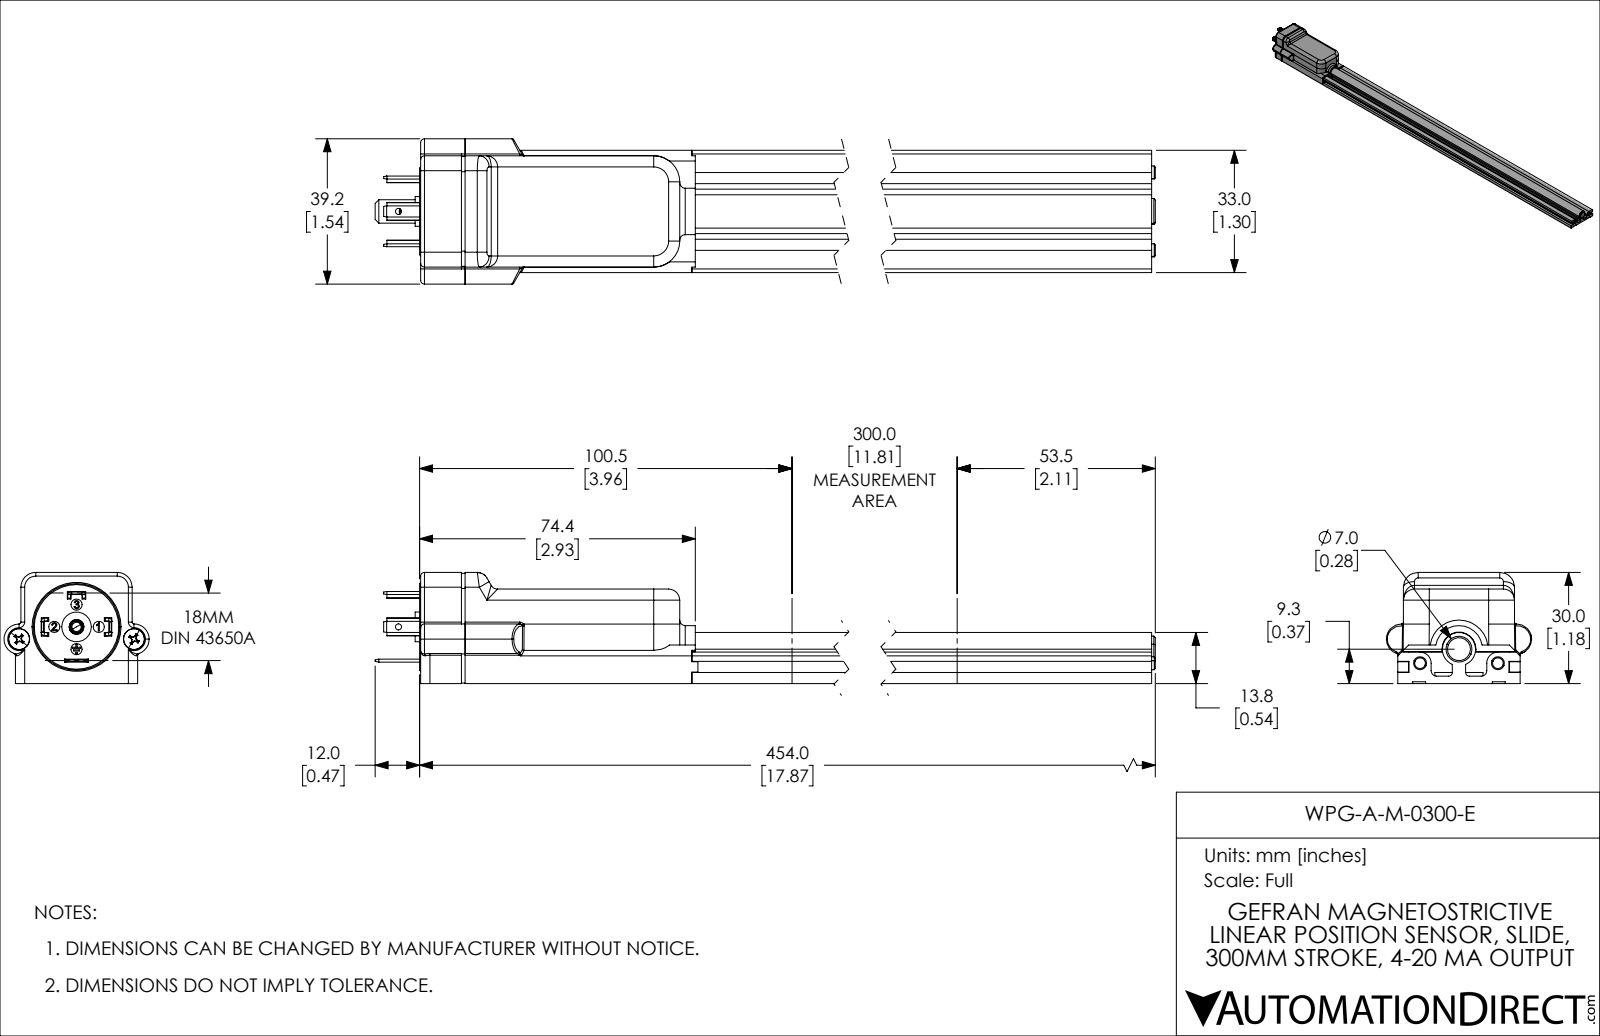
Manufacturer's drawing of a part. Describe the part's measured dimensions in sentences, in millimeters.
The part is named "WPG-A-M-0300-E". Its 3-D file was written by "SolidWorks 2021 (CONFIG_CONTROL_DESIGN)". It is 15 solids with 589 faces: 371 planar, 139 cylindrical and 79 other. Overall it measures 466 by 39.2 by 30 millimeters. Its volume is 148 171 cubic millimeters and its surface area 67 199 square millimeters. Round holes: 5 of diameter 3, 2 of diameter 1.5, 2 of diameter 1.65, 2 of diameter 3.2, 2 of diameter 5.7, 1 of diameter 1.6, 1 of diameter 2.5, 1 of diameter 4. Round bosses or shafts: 2 of diameter 5.6, 2 of diameter 3.5, 2 of diameter 2.85, 1 of diameter 9, 1 of diameter 8, 1 of diameter 7, 1 of diameter 5.3, 1 of diameter 3.94. Partial cylindrical surfaces (rounded edges, fillets, slot ends): 8 of radius 0.5, 8 of radius 3, 6 of radius 0.85, 5 of radius 1, 4 of radius 0.8, 4 of radius 1.5, 4 of radius 4.1, 4 of radius 7. The main face-to-face distances are 3, 1, 2.5, 1.5, 5.5, 6, 8.5, 30, 0.5, 8. The hole center spacings are 6, 8.49, 10.06, 12, 12.3, 15.73, 15.85, 18.08.
